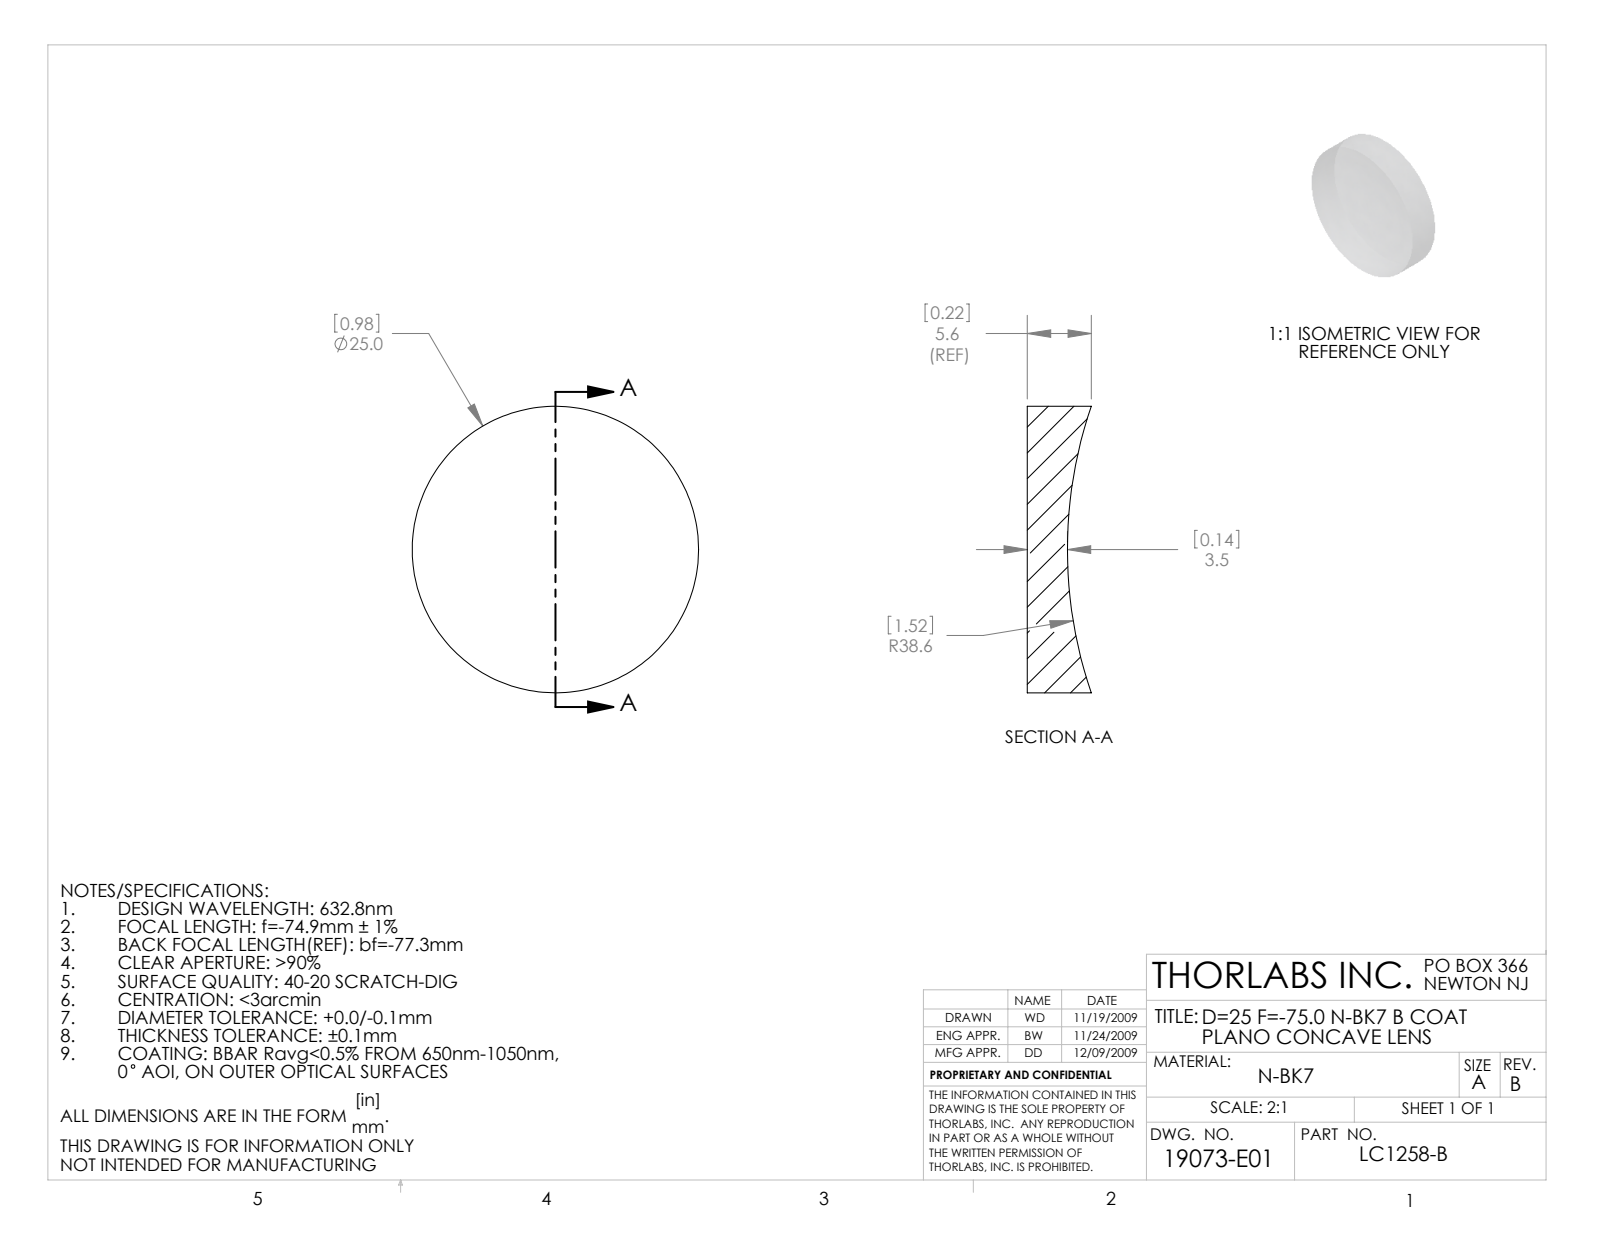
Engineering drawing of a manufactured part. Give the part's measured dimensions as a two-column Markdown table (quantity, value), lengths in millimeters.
| quantity | value |
| --- | --- |
| part name | 19073-E0W |
| STEP written by | SolidWorks 2009 (AUTOMOTIVE_DESIGN) |
| units | millimeters |
| bodies | 1 solid, 5 faces (1 planar, 2 cylindrical, 2 other) |
| overall size | 25 × 25 × 5.58 |
| volume | 2 224 mm³ |
| surface area | 1 434 mm² |
| round bosses / shafts (diameter × count) | 25 × 1 |
